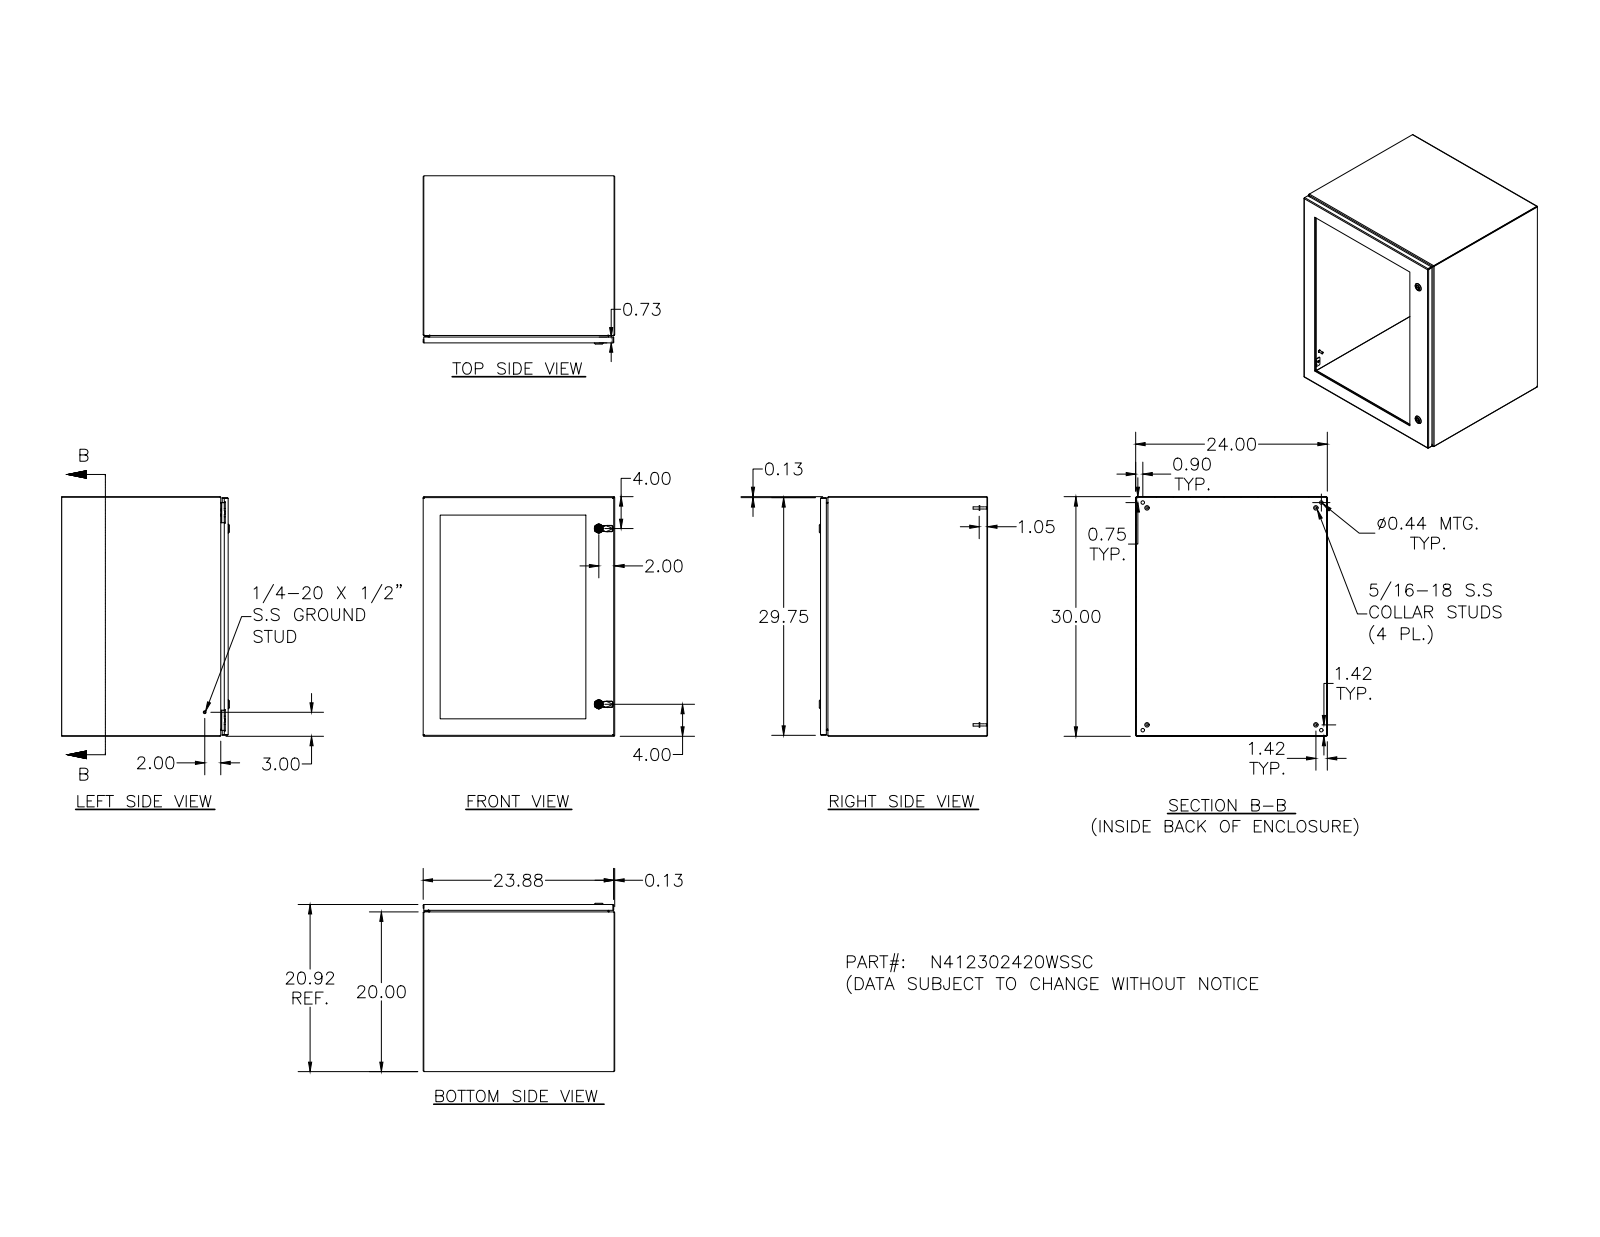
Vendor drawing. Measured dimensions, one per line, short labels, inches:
name: N412302420WSSC; N4123024WSSCLID; 36823; 36825 (+8 more)
written by: Autodesk Inventor 2011 (AUTOMOTIVE_DESIGN)
unit: in
bodies: 96 solids, 2506 faces (1041 planar, 684 cylindrical, 781 other)
size: 30 × 24 × 21.075
volume: 382.9 in³; area: 8 003 in²
holes: 26× ⌀0.156, 24× ⌀0.281, 4× ⌀0.093, 4× ⌀0.152, 4× ⌀0.167, 4× ⌀0.172, 4× ⌀0.187, 4× ⌀0.437, 2× ⌀0.197, 2× ⌀0.315, 2× ⌀0.394, 2× ⌀0.402
bosses: 24× ⌀0.19, 23× ⌀0.253, 10× ⌀0.25, 4× ⌀0.563, 4× ⌀0.36, 4× ⌀0.32, 4× ⌀0.3, 4× ⌀0.275
rounds: 32× R0.031, 26× R0.05, 22× R0.105, 18× R0.016, 16× R0.125, 15× R0.02, 8× R0.032, 8× R0.157
face distances: 0.074, 23.926, 29.926, 20.843, 20.769, 23.852, 24, 0.25, 20.593, 20.519
hole spacings: 4, 8, 12, 19.906, 21.077, 16, 22.896, 27.047
